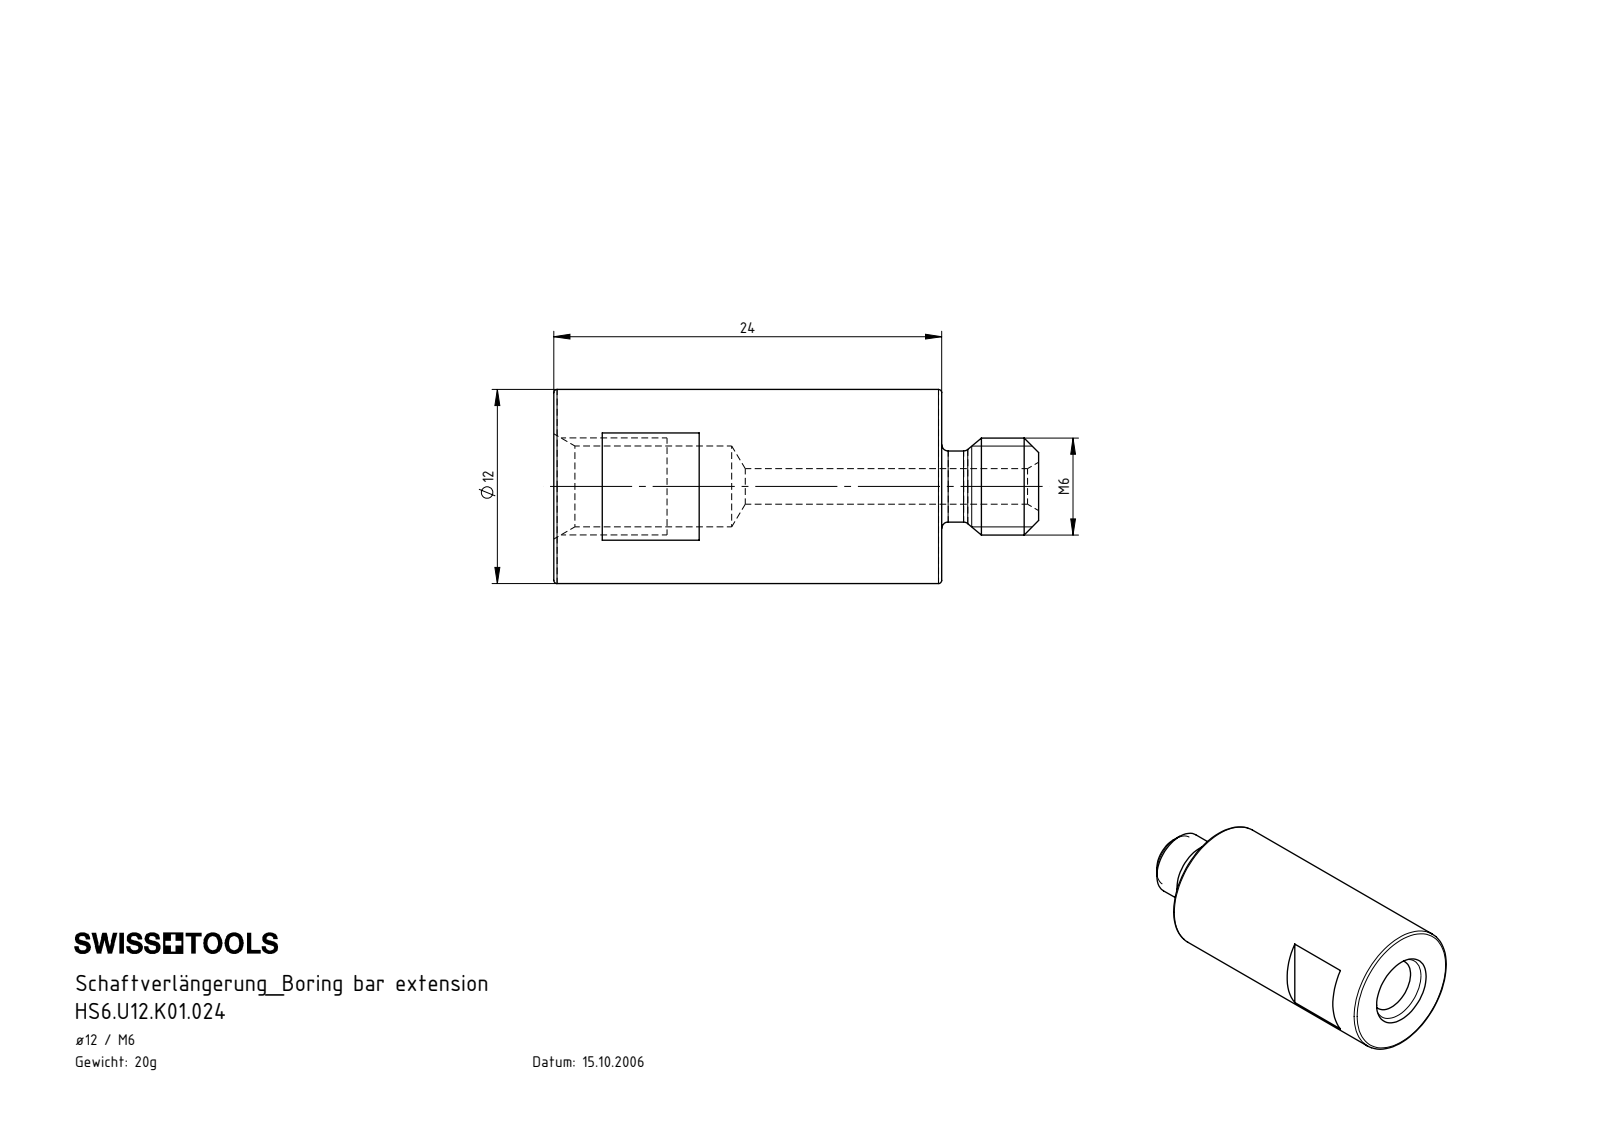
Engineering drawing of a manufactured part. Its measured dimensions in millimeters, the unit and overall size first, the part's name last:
Units: millimetres
Overall size (bounding box): 30 × 12 × 12
Round holes (diameter × count): ⌀2.2 ×1, ⌀5 ×1
Round bosses / shafts (diameter × count): ⌀12 ×1, ⌀6 ×1, ⌀4.4 ×1
Main face-to-face distances: 24, 10, 21, 6, 3, 15, 9, 27, 30
Volume: 2 493 mm³ · Surface area: 1 530 mm²
Bodies: 1 solid, 37 faces (9 planar, 10 cylindrical, 18 other)
Part name (STEP PRODUCT): HS6.U12.K01.024
STEP written by: SolidWorks 2022 (CONFIG_CONTROL_DESIGN)
